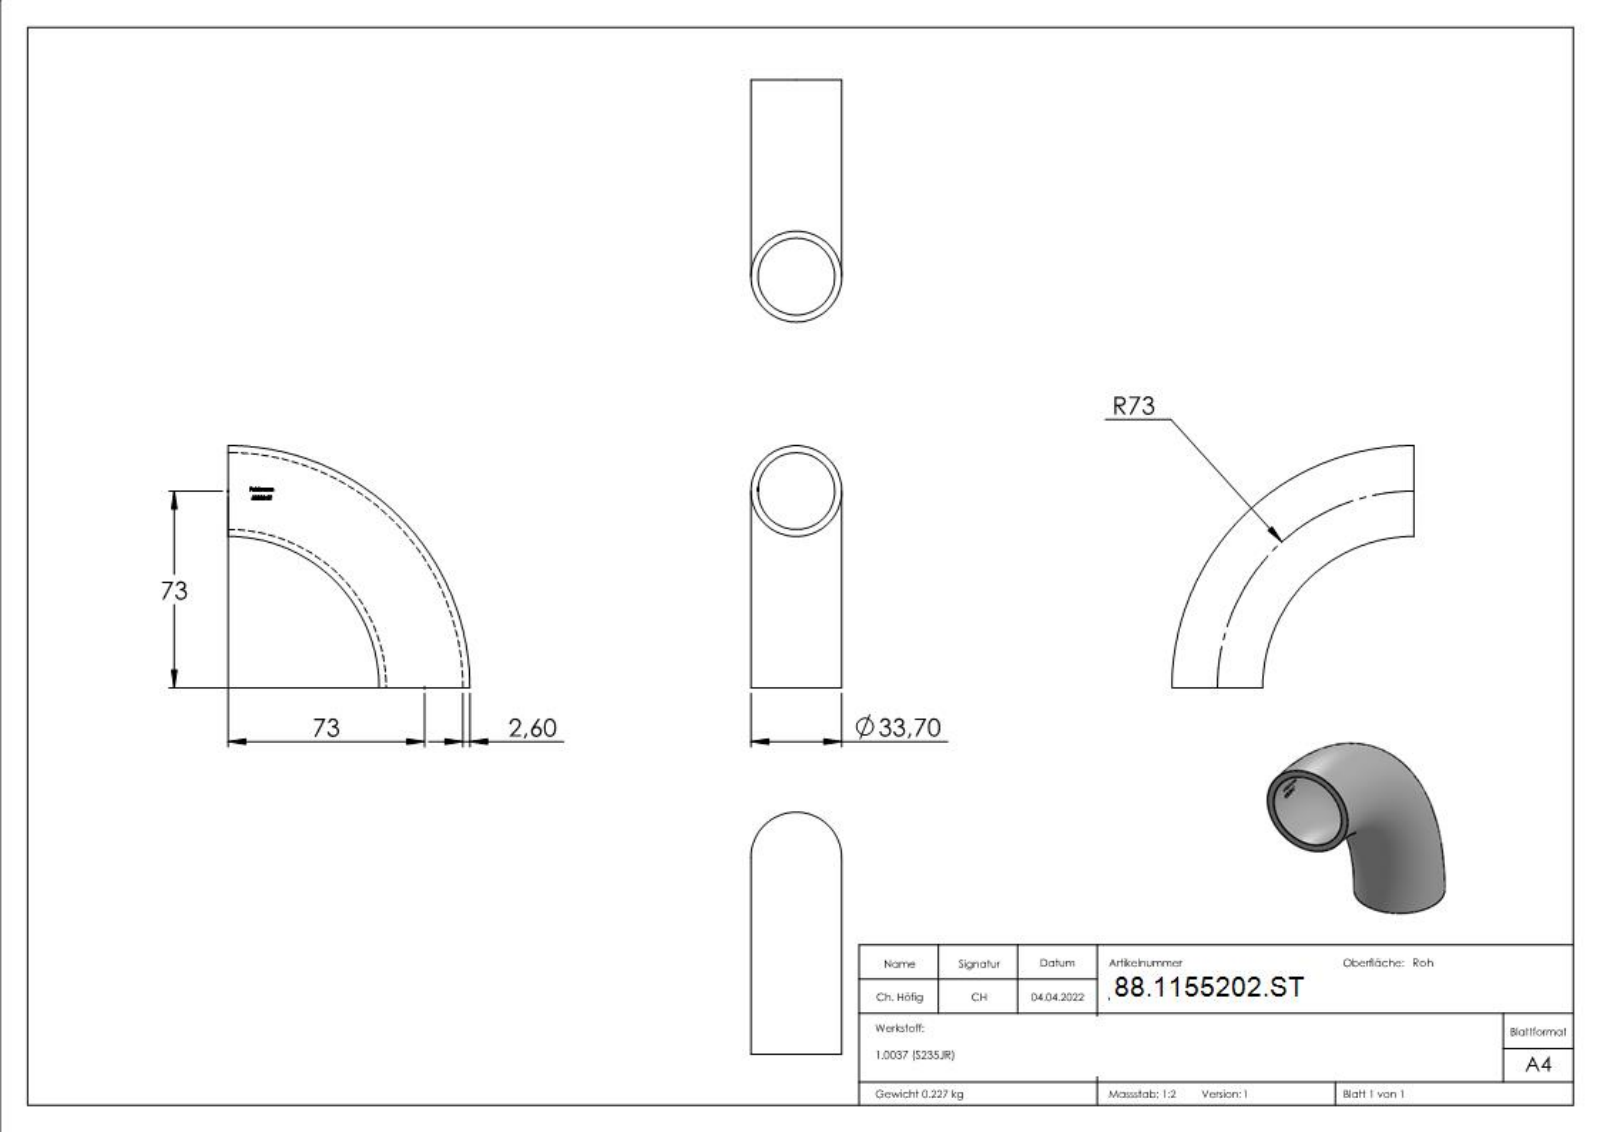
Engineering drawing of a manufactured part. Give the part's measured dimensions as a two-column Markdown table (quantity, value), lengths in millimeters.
| quantity | value |
| --- | --- |
| part name | 55202-ST |
| STEP written by | SolidWorks 2018 (CONFIG_CONTROL_DESIGN) |
| units | millimeters |
| bodies | 1 solid, 216 faces (94 planar, 0 cylindrical, 122 other) |
| overall size | 89.85 × 89.85 × 33.7 |
| volume | 29 129 mm³ |
| surface area | 22 924 mm² |
| main face-to-face distances | 1.32, 0.39, 2.97, 1.12, 2.02, 3.66, 3.27, 7.52, 5.62, 3.07 |
